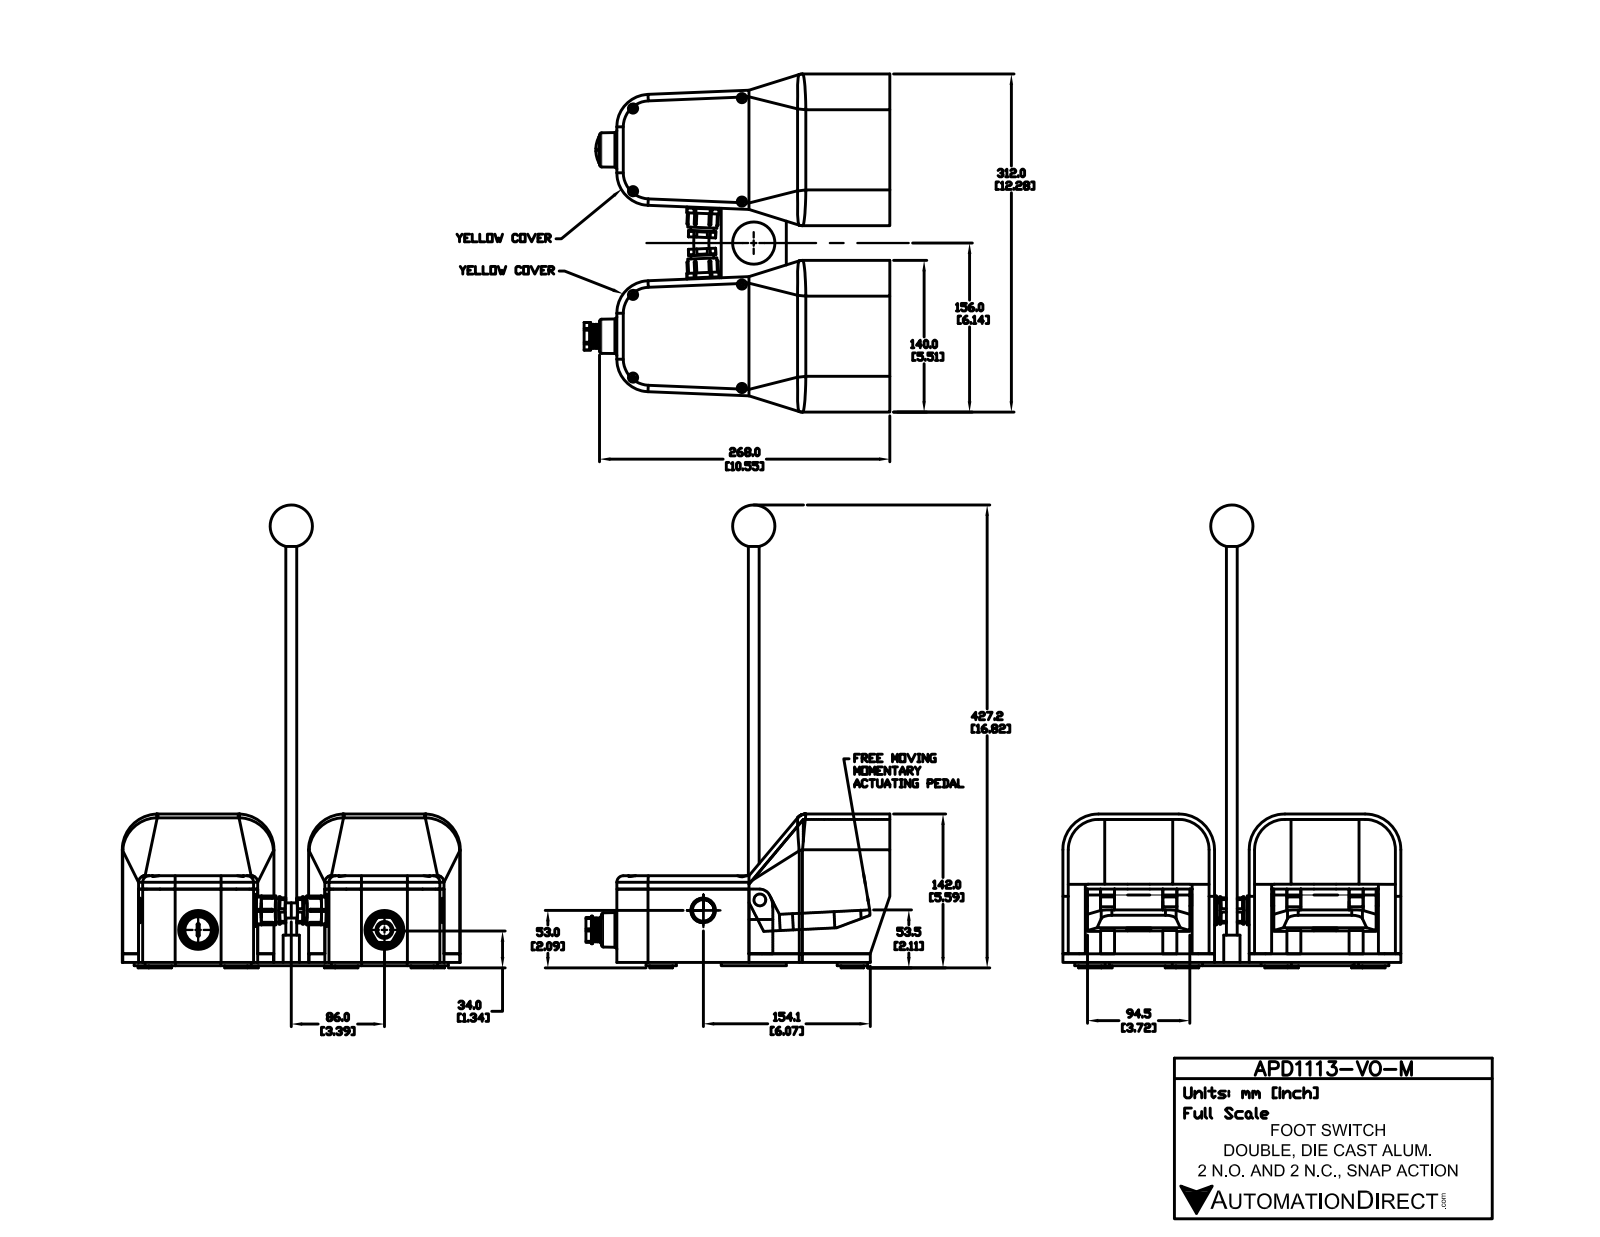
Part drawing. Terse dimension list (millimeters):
name: APD1113-V0-M
written by: SolidWorks 2015 (AUTOMOTIVE_DESIGN)
unit: mm
bodies: 36 solids, 829 faces (502 planar, 213 cylindrical, 114 other)
size: 427.2 × 312 × 282.2
volume: 3 215 000 mm³; area: 575 900 mm²
holes: 8× ⌀8.5, 4× ⌀22.8, 1× ⌀12.6, 1× ⌀15.6
bosses: 8× ⌀28, 8× ⌀21, 4× ⌀19.9, 2× ⌀29.7, 2× ⌀26.7, 2× ⌀25.2, 2× ⌀21.5, 1× ⌀25.5
rounds: 34× R1, 12× R1.1, 10× R10, 5× R6, 4× R28, 4× R30, 4× R33, 1× R20
face distances: 5, 135, 172, 8, 59.6, 140, 67.7, 59.7, 67.6, 3
hole spacings: 101, 132.2, 172, 76.3, 95.5, 132.4, 191, 207.6
